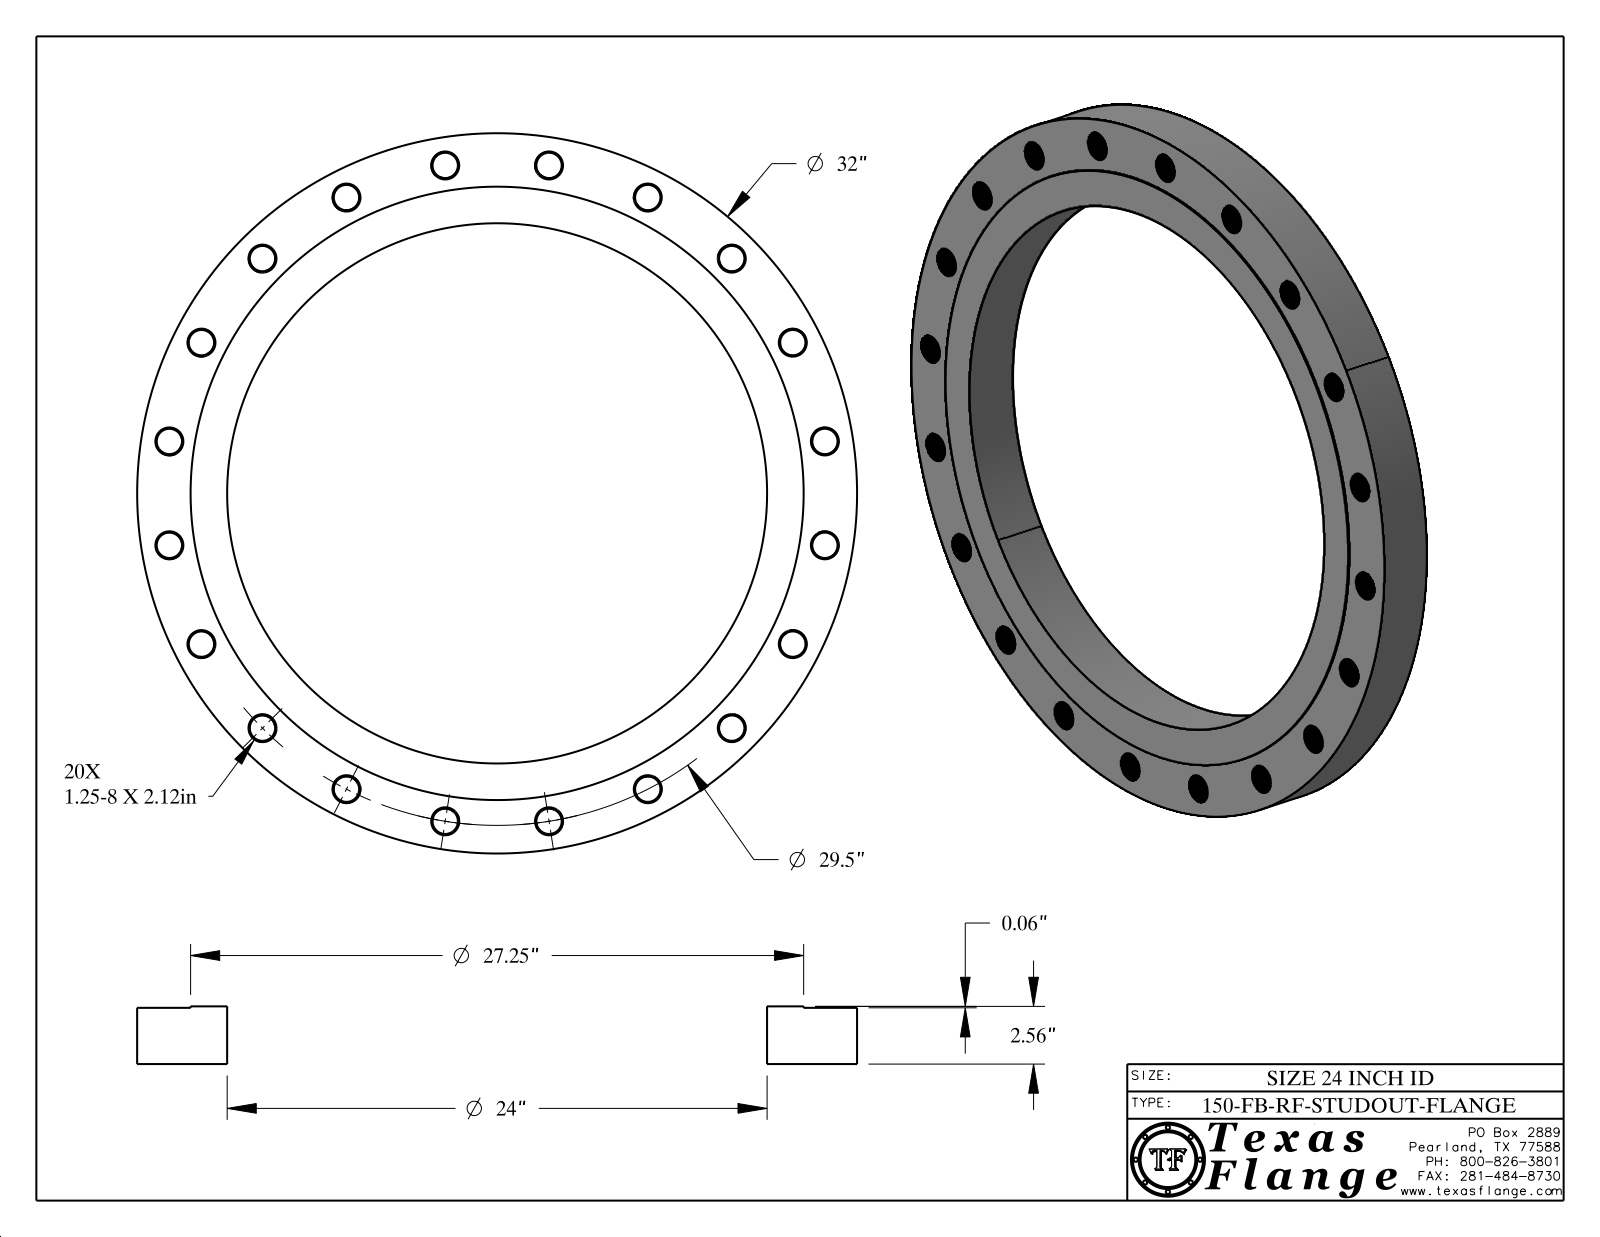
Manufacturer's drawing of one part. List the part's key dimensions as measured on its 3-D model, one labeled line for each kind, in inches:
Part name (STEP PRODUCT): 24-150-FB-RF-STUDOUT-FLANGE
STEP written by: CATIA V5 STEP AP214 (AUTOMOTIVE_DESIGN)
Units: inches
Bodies: 1 solid, 1954 faces (368 planar, 506 cylindrical, 1080 other)
Overall size (bounding box): 32 × 32 × 2.563
Volume: 840.4 in³ · Surface area: 1 351 in²
Round holes (diameter × count): ⌀1.125 ×20, ⌀1 ×1, ⌀24 ×1
Round bosses / shafts (diameter × count): ⌀0.061 ×8, ⌀32 ×1, ⌀27.25 ×1, ⌀0.788 ×1
Main face-to-face distances: 2.5, 0.063, 2.563, 2.548, 2.485, 0.015, 0.298, 0.293, 0.054, 0.248
Hole centre spacings: 4.615, 9.116, 13.393, 17.34, 20.86, 23.866, 26.285, 29.137
